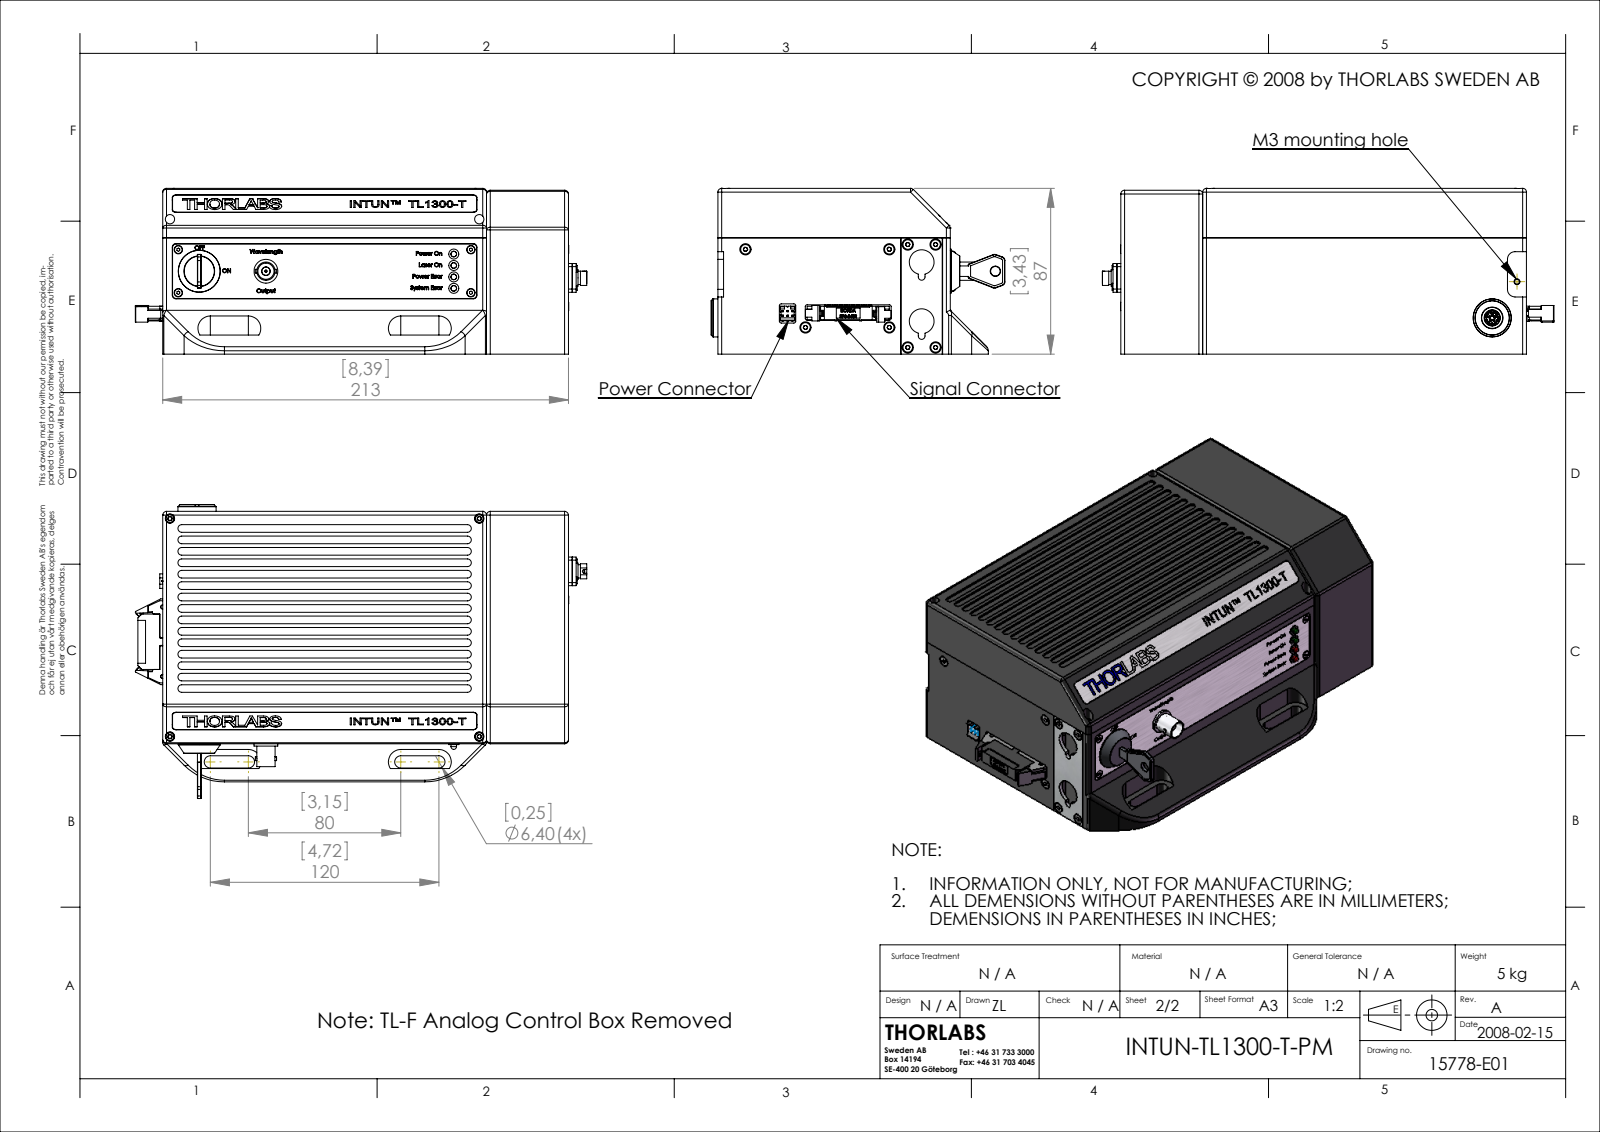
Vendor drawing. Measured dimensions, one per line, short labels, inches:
name: INTUN-TL1300-T-PM
written by: SolidWorks 2007 (CONFIG_CONTROL_DESIGN)
unit: in
bodies: 0 solids, 7651 faces (5117 planar, 1286 cylindrical, 1248 other)
size: 12.386 × 6.071 × 4.343
holes: 33× ⌀0.039, 17× ⌀0.106, 12× ⌀0.063, 12× ⌀0.081, 12× ⌀0.094, 8× ⌀0.114, 8× ⌀0.193, 6× ⌀0.087, 6× ⌀0.433, 5× ⌀0.118, 5× ⌀0.169, 5× ⌀0.177
bosses: 13× ⌀0.079, 12× ⌀0.098, 8× ⌀0.157, 7× ⌀0.177, 6× ⌀0.224, 6× ⌀0.209, 6× ⌀0.197, 6× ⌀0.118
rounds: 100× R0.079, 41× R0.197, 20× R0.006, 20× R0.039, 16× R0.071, 14× R0.008, 12× R0.039, 12× R0.236
face distances: 0.197, 0.039, 0.079, 0.118, 0.236, 0.246, 3.425, 3.386, 3.189, 0.157
hole spacings: 0.126, 0.136, 0.191, 0.25, 0.374, 0.876, 0.876, 0.071
